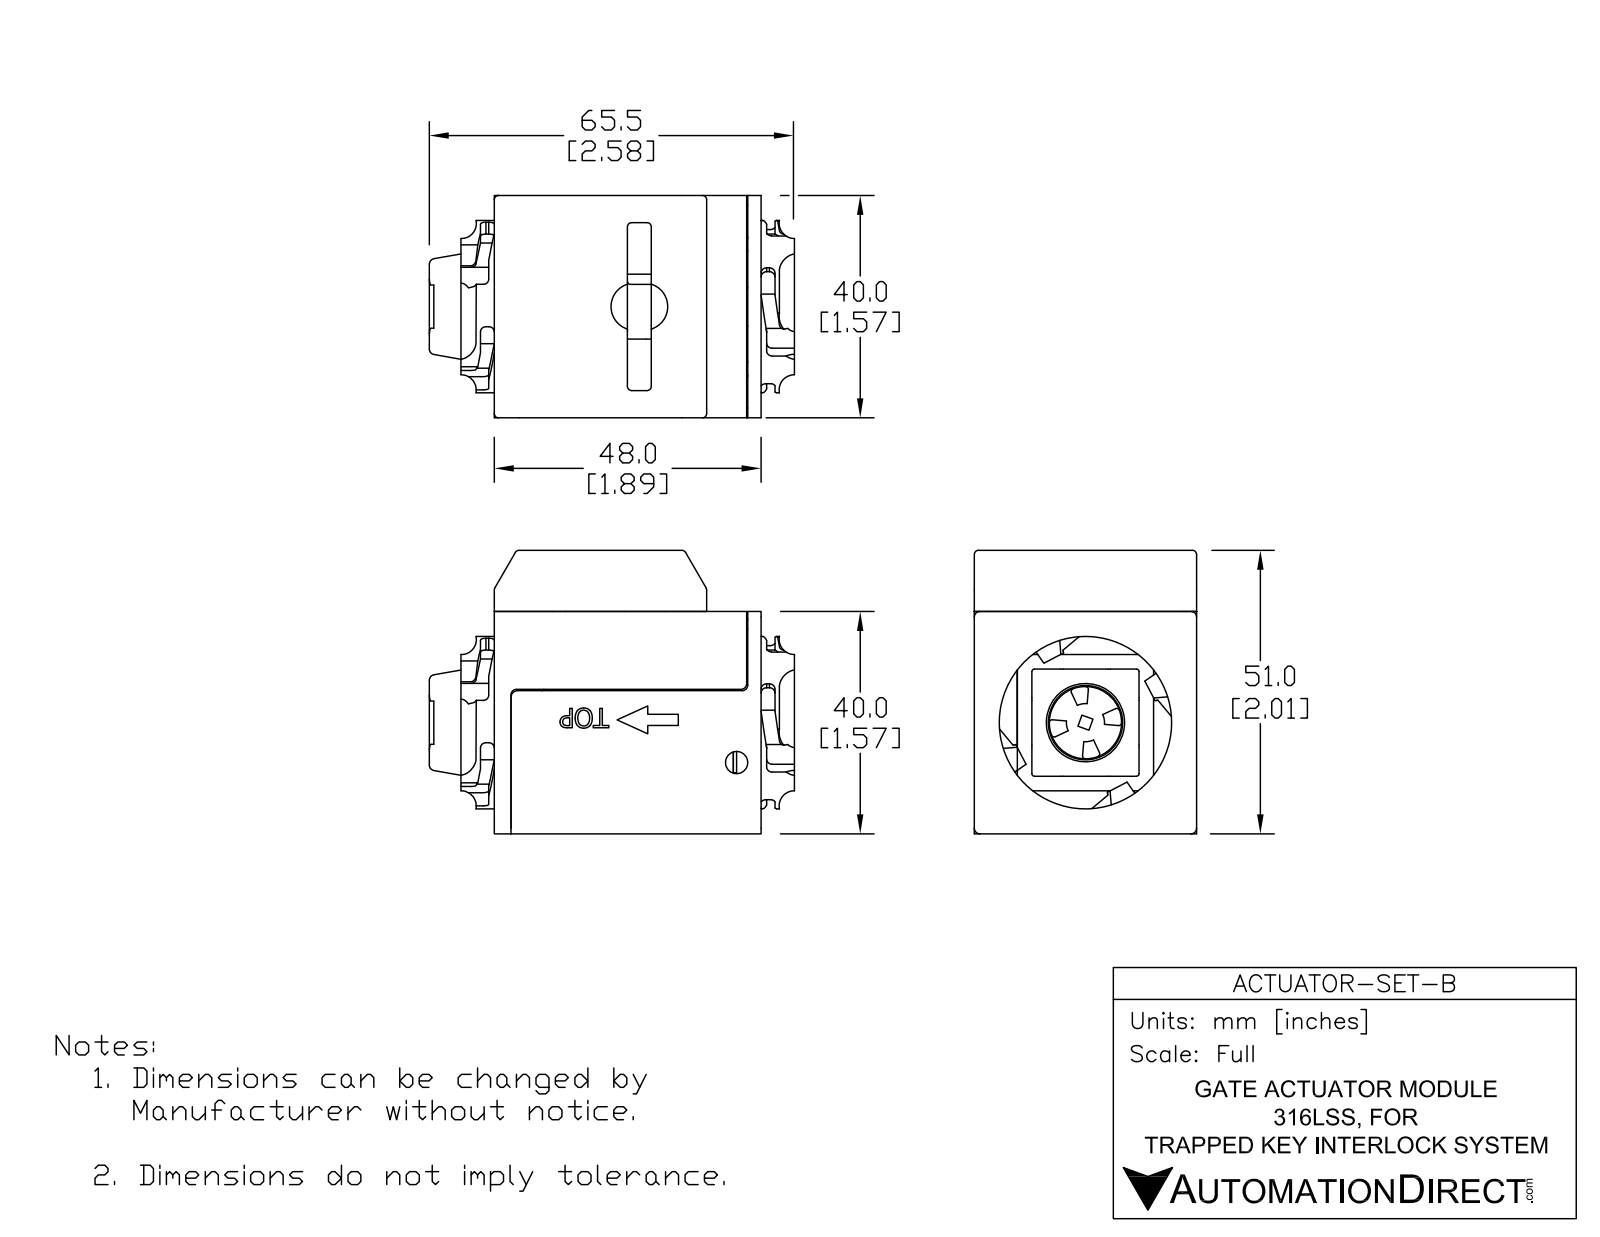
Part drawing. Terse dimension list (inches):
name: ACTUATOR-SET-B
written by: SolidWorks 2017 (AUTOMOTIVE_DESIGN)
unit: in
bodies: 2 solids, 1198 faces (547 planar, 75 cylindrical, 576 other)
size: 2.559 × 2.008 × 1.585
volume: 6.545 in³; area: 32.1 in²
holes: 2× ⌀0.097, 2× ⌀0.157, 2× ⌀0.217
bosses: 1× ⌀0.394
rounds: 30× R0.03, 14× R0.039, 6× R0.02, 2× R0.167, 2× R0.217
face distances: 1.575, 1.89, 2.362, 0.472, 1.575, 0.433, 2.008, 0.433, 1.569, 1.569
hole spacings: 0.571, 1.181, 1.219, 1.569
